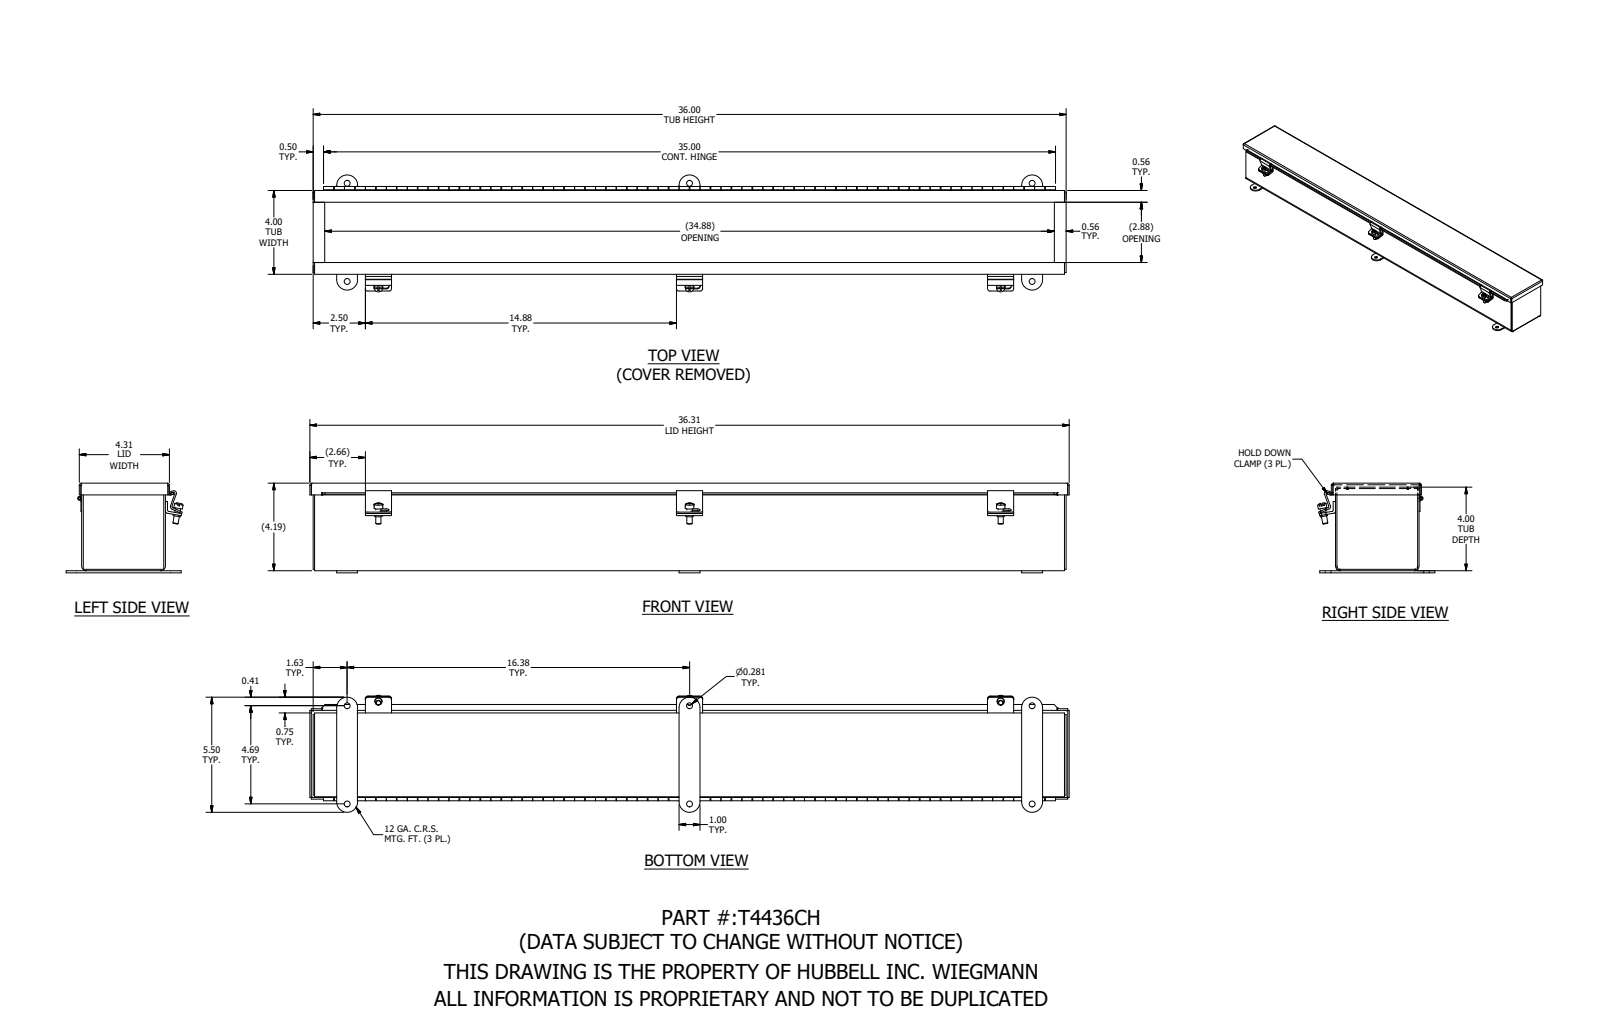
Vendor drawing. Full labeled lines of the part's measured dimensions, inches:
Part name (STEP PRODUCT): T4436CH
STEP written by: SolidWorks 2021 (AUTOMOTIVE_DESIGN)
Units: inches
Bodies: 19 solids, 825 faces (414 planar, 388 cylindrical, 23 other)
Overall size (bounding box): 36.313 × 5.595 × 4.283
Volume: 55.62 in³ · Surface area: 1 569 in²
Round holes (diameter × count): ⌀0.281 ×6, ⌀0.196 ×3, ⌀0.116 ×1
Round bosses / shafts (diameter × count): ⌀0.41 ×3, ⌀0.344 ×3, ⌀0.25 ×3, ⌀0.2 ×1, ⌀0.1 ×1
Partial cylindrical surfaces — rounded edges, fillets, slot ends (radius × count): R0.125 ×12, R0.031 ×9, R0.105 ×9, R0.133 ×6, R0.5 ×6, R0.063 ×3, R0.126 ×3, R0.156 ×2
Main face-to-face distances: 0.074, 3.926, 4.115, 4, 3.852, 4.189, 4.041, 0.189, 4.042, 0.116
Hole centre spacings: 4.687, 16.375, 16.375, 17.033, 17.033, 32.75, 33.084, 14.875
